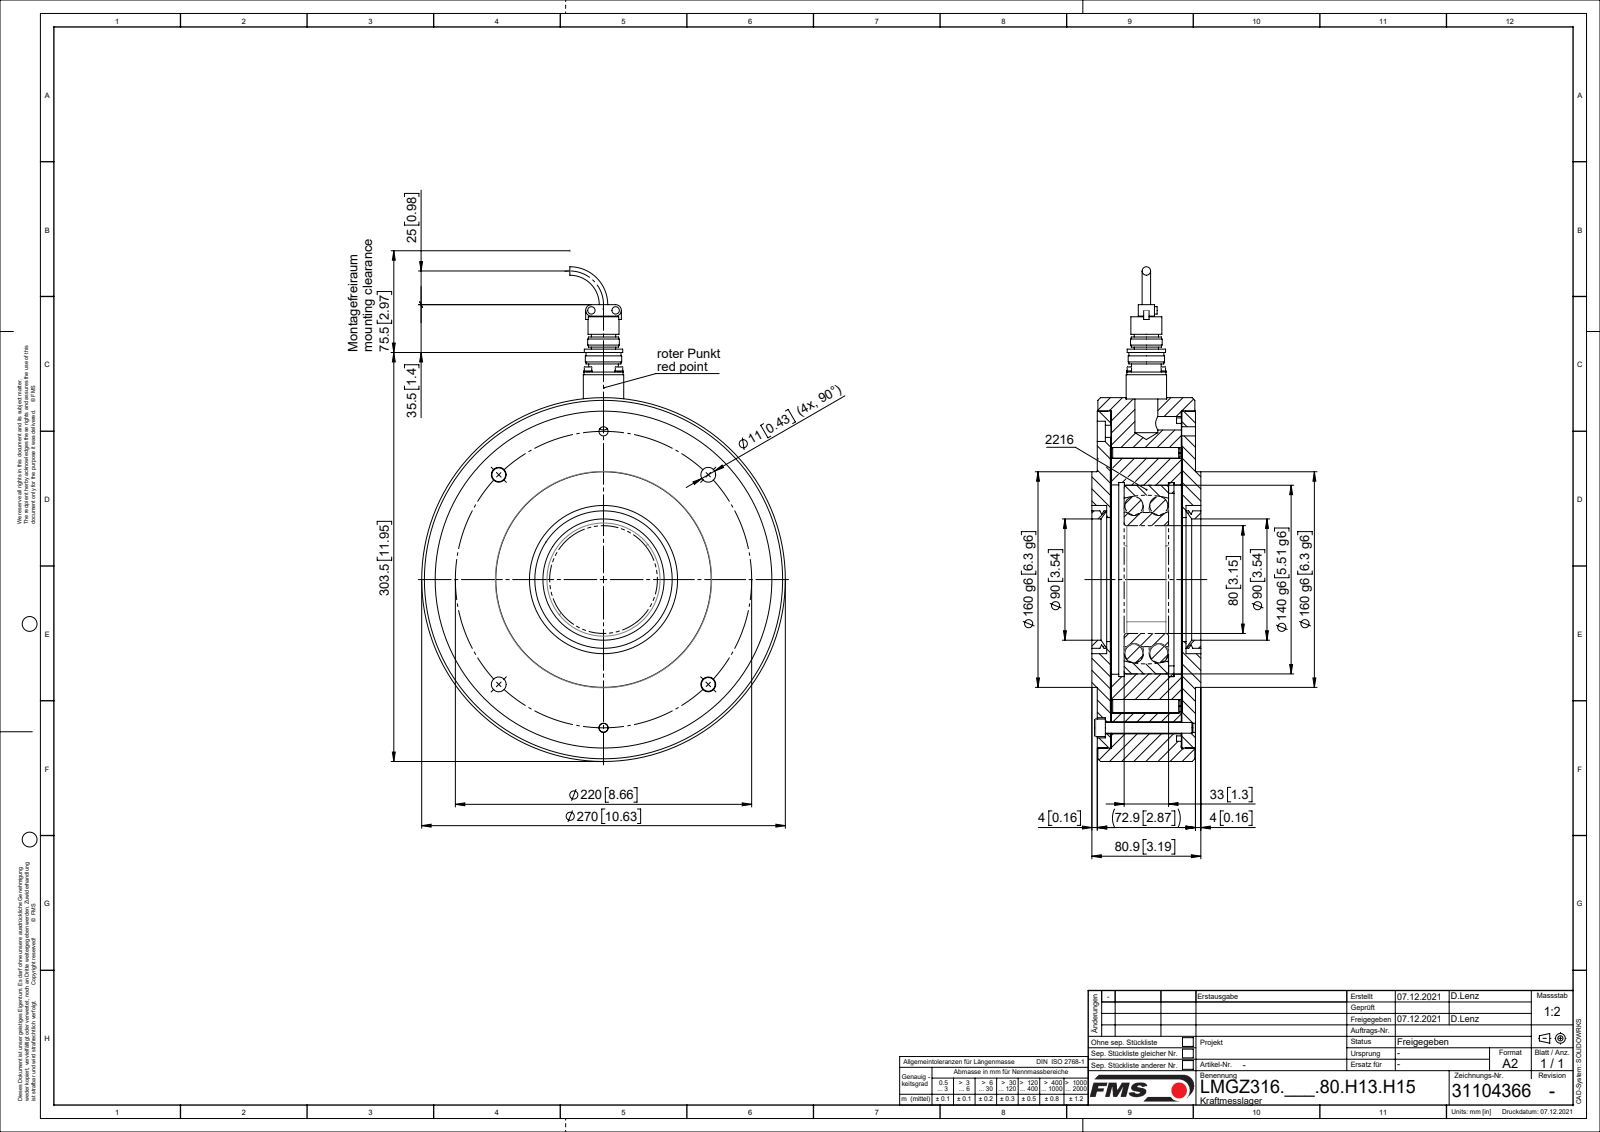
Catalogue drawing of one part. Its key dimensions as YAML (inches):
part_name: "31104366_Stp; 31101677_V-090A; 49492.03_stp_01; FLANSCHDOSE_14S-2P_4-POLIG (+8 more)"
step_written_by: "SolidWorks 2018 (CONFIG_CONTROL_DESIGN)"
units: inches
bodies: {solids: 61, faces: 588, planar: 146, cylindrical: 272, other: 170}
overall_size: [14.455, 10.63, 3.185]
volume: 207.7
surface_area: 966.5
round_holes:
  - {diameter: 0.098, count: 4}
  - {diameter: 0.122, count: 4}
  - {diameter: 0.134, count: 4}
  - {diameter: 0.394, count: 4}
  - {diameter: 0.433, count: 4}
  - {diameter: 0.472, count: 4}
  - {diameter: 0.945, count: 4}
  - {diameter: 0.157, count: 2}
  - {diameter: 0.268, count: 2}
  - {diameter: 0.354, count: 2}
  - {diameter: 0.402, count: 2}
  - {diameter: 0.591, count: 2}
round_bosses_or_shafts:
  - {diameter: 0.217, count: 6}
  - {diameter: 0.244, count: 4}
  - {diameter: 0.118, count: 4}
  - {diameter: 0.098, count: 4}
  - {diameter: 10.63, count: 1}
  - {diameter: 9.843, count: 1}
  - {diameter: 9.134, count: 1}
  - {diameter: 6.299, count: 1}
partial_cylinders:
  - {radius: 0.004, count: 4}
  - {radius: 0.167, count: 2}
  - {radius: 0.228, count: 2}
  - {radius: 2.394, count: 1}
face_to_face_distances: [2.057, 0.402, 0.411, 2.459, 2.469, 2.067, 0.02, 0.382, 2.488, 0.03]
hole_center_spacings: [4.331, 0.64, 0.906, 3.128, 3.315, 3.976, 6.124, 7.424]
